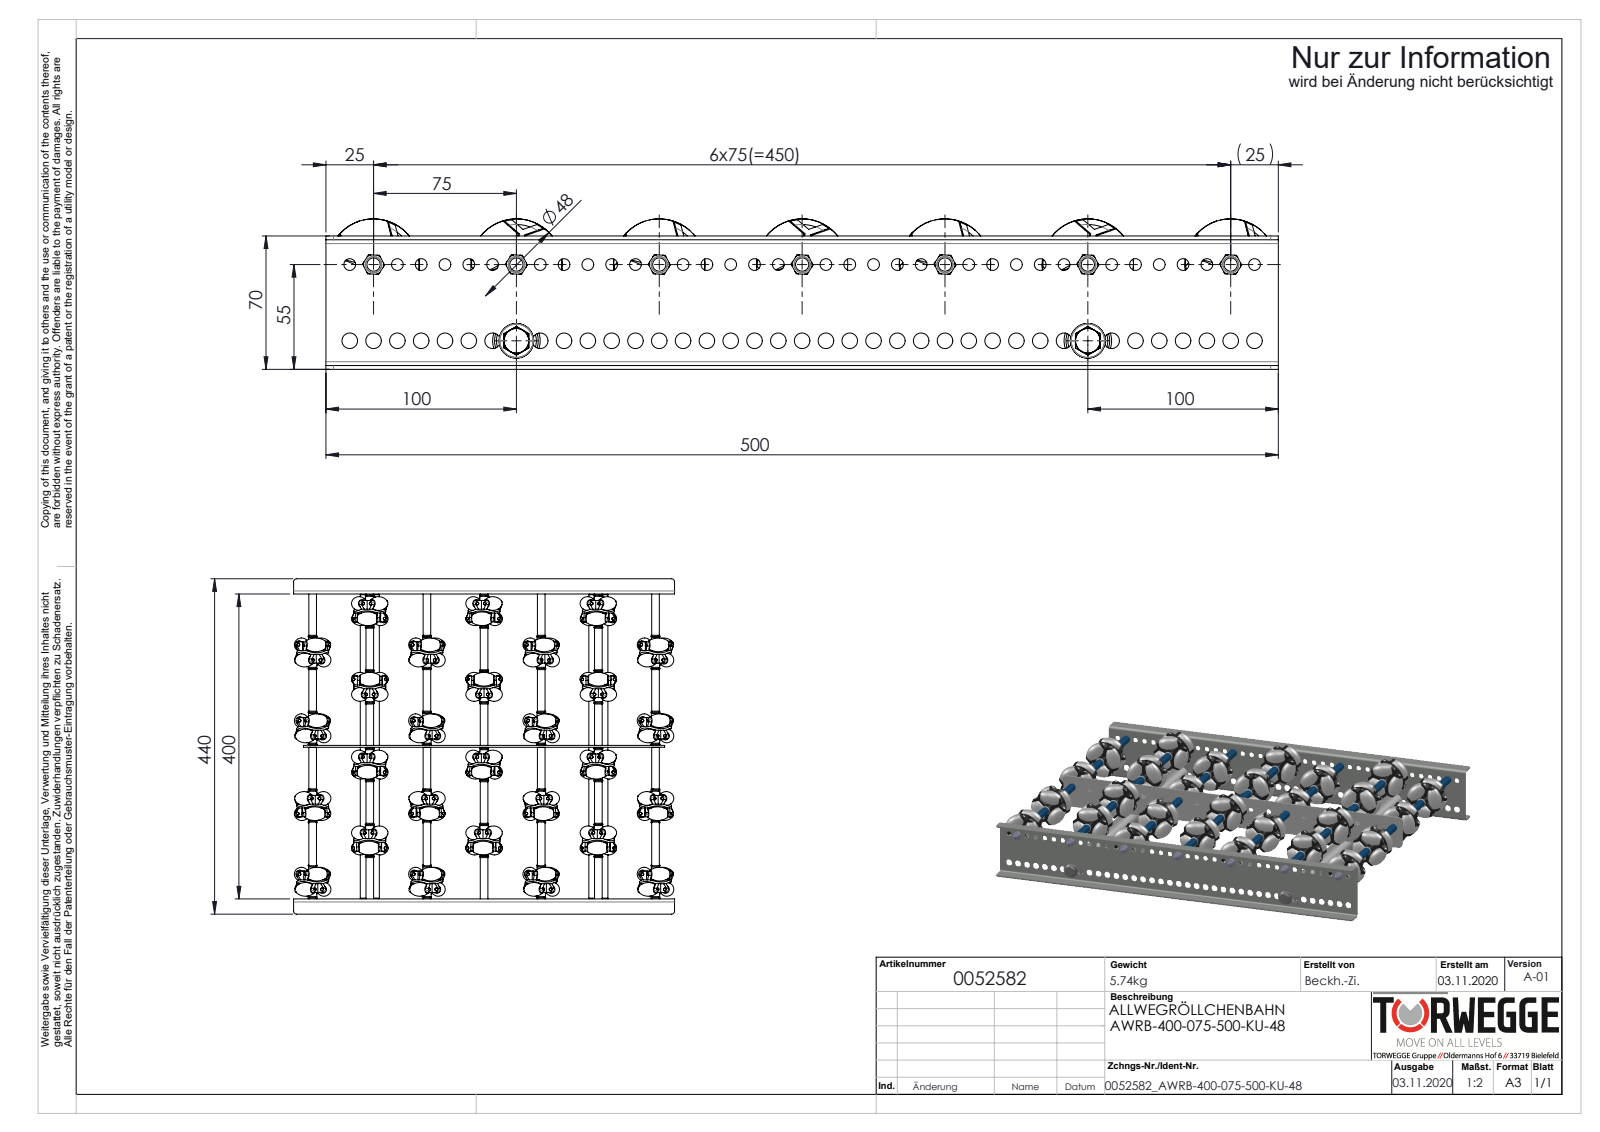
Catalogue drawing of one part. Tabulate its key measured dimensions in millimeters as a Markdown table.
| quantity | value |
| --- | --- |
| part name | 0027528_BUCHSE-HOHLNIETE ZU AWR48; 0015028_AWR48; Profil-RB-20x70x20x2_S100208_U-PROFIL-20-70-20-2-RB-L=500; AWR48_Halter (+8 more) |
| STEP written by | SolidWorks 2020 (AUTOMOTIVE_DESIGN) |
| units | millimeters |
| bodies | 482 solids, 8718 faces (2996 planar, 3392 cylindrical, 2330 other) |
| overall size | 500 × 440 × 79 |
| volume | 1 732 000 mm³ |
| surface area | 1 224 000 mm² |
| round holes (diameter × count) | 3.7 × 168, 4.2 × 168, 6.2 × 39, 8.2 × 39, 6.5 × 19, 4.92 × 7, 8.4 × 7, 6.8 × 2, 21 × 2 |
| round bosses / shafts (diameter × count) | 4 × 168, 3.7 × 136, 8 × 9, 42 × 7, 11 × 7, 10 × 7, 7 × 7, 6 × 7 |
| partial cylindrical surfaces (radius × count) | 4 × 8, 23.55 × 7, 2 × 4, 5 × 4 |
| main face-to-face distances | 2, 402, 68, 400, 404, 200.6, 198.6, 201.4, 203.4, 203.1 |
| hole center spacings | 36.06, 36.05, 12.5, 25, 37.5, 87.5, 36.04, 50 |
